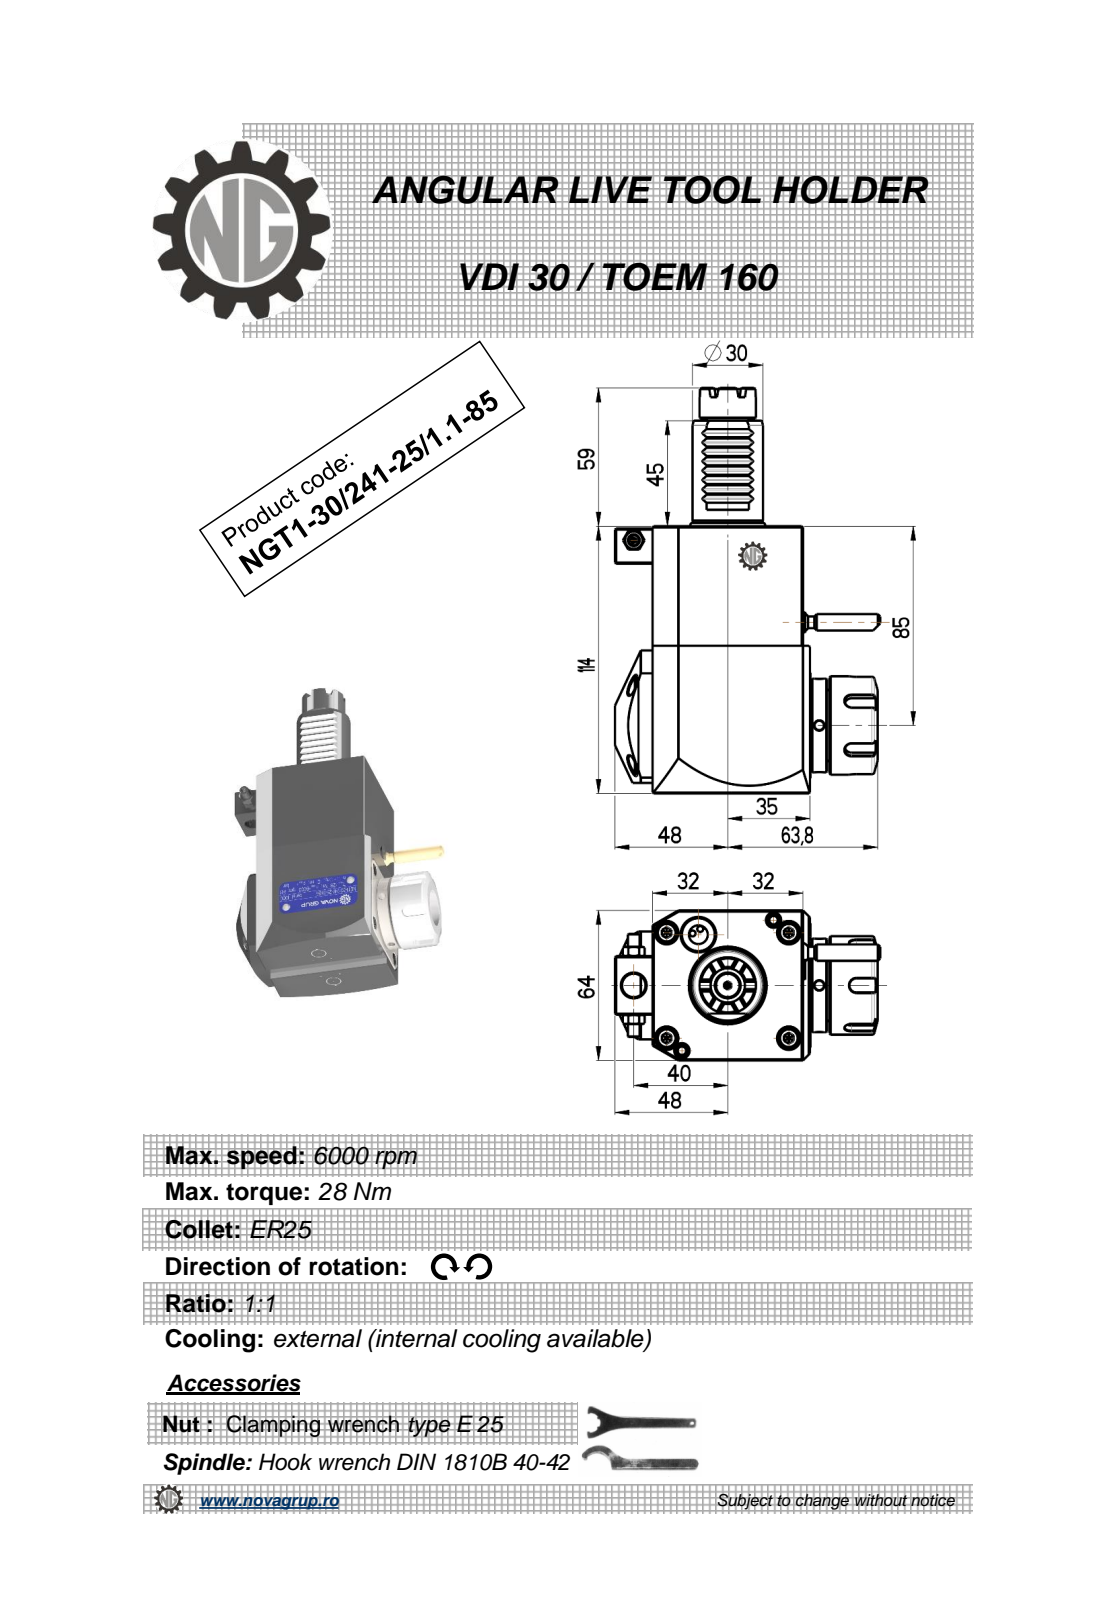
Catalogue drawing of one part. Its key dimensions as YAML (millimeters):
part_name: "NGT1_30_241_25_1_1_85"
step_written_by: "PRO/ENGINEER BY PARAMETRIC TECHNOLOGY CORPORATION, 2010280 (CONFIG_CONTROL_DESIGN)"
units: millimeters
bodies: {solids: 1, faces: 455, planar: 210, cylindrical: 92, other: 153}
overall_size: [173, 112.88, 65.6]
volume: 569516
surface_area: 53758
round_holes:
  - {diameter: 4, count: 2}
  - {diameter: 2.5, count: 1}
  - {diameter: 3, count: 1}
  - {diameter: 4.2, count: 1}
  - {diameter: 9.5, count: 1}
  - {diameter: 10, count: 1}
  - {diameter: 20.3, count: 1}
round_bosses_or_shafts:
  - {diameter: 8.96, count: 2}
  - {diameter: 5, count: 2}
  - {diameter: 42, count: 1}
  - {diameter: 40, count: 1}
  - {diameter: 33, count: 1}
  - {diameter: 30, count: 1}
  - {diameter: 24, count: 1}
  - {diameter: 17.7, count: 1}
partial_cylinders:
  - {radius: 0.26, count: 12}
  - {radius: 0.3, count: 8}
  - {radius: 3, count: 5}
  - {radius: 3.5, count: 2}
  - {radius: 160, count: 2}
  - {radius: 7.6, count: 1}
  - {radius: 32, count: 1}
face_to_face_distances: [64, 114, 67.2, 3.2, 67, 3, 0.5, 16, 110, 4]
hole_center_spacings: [35.39, 46.17, 76.5, 78.95, 111.69]
